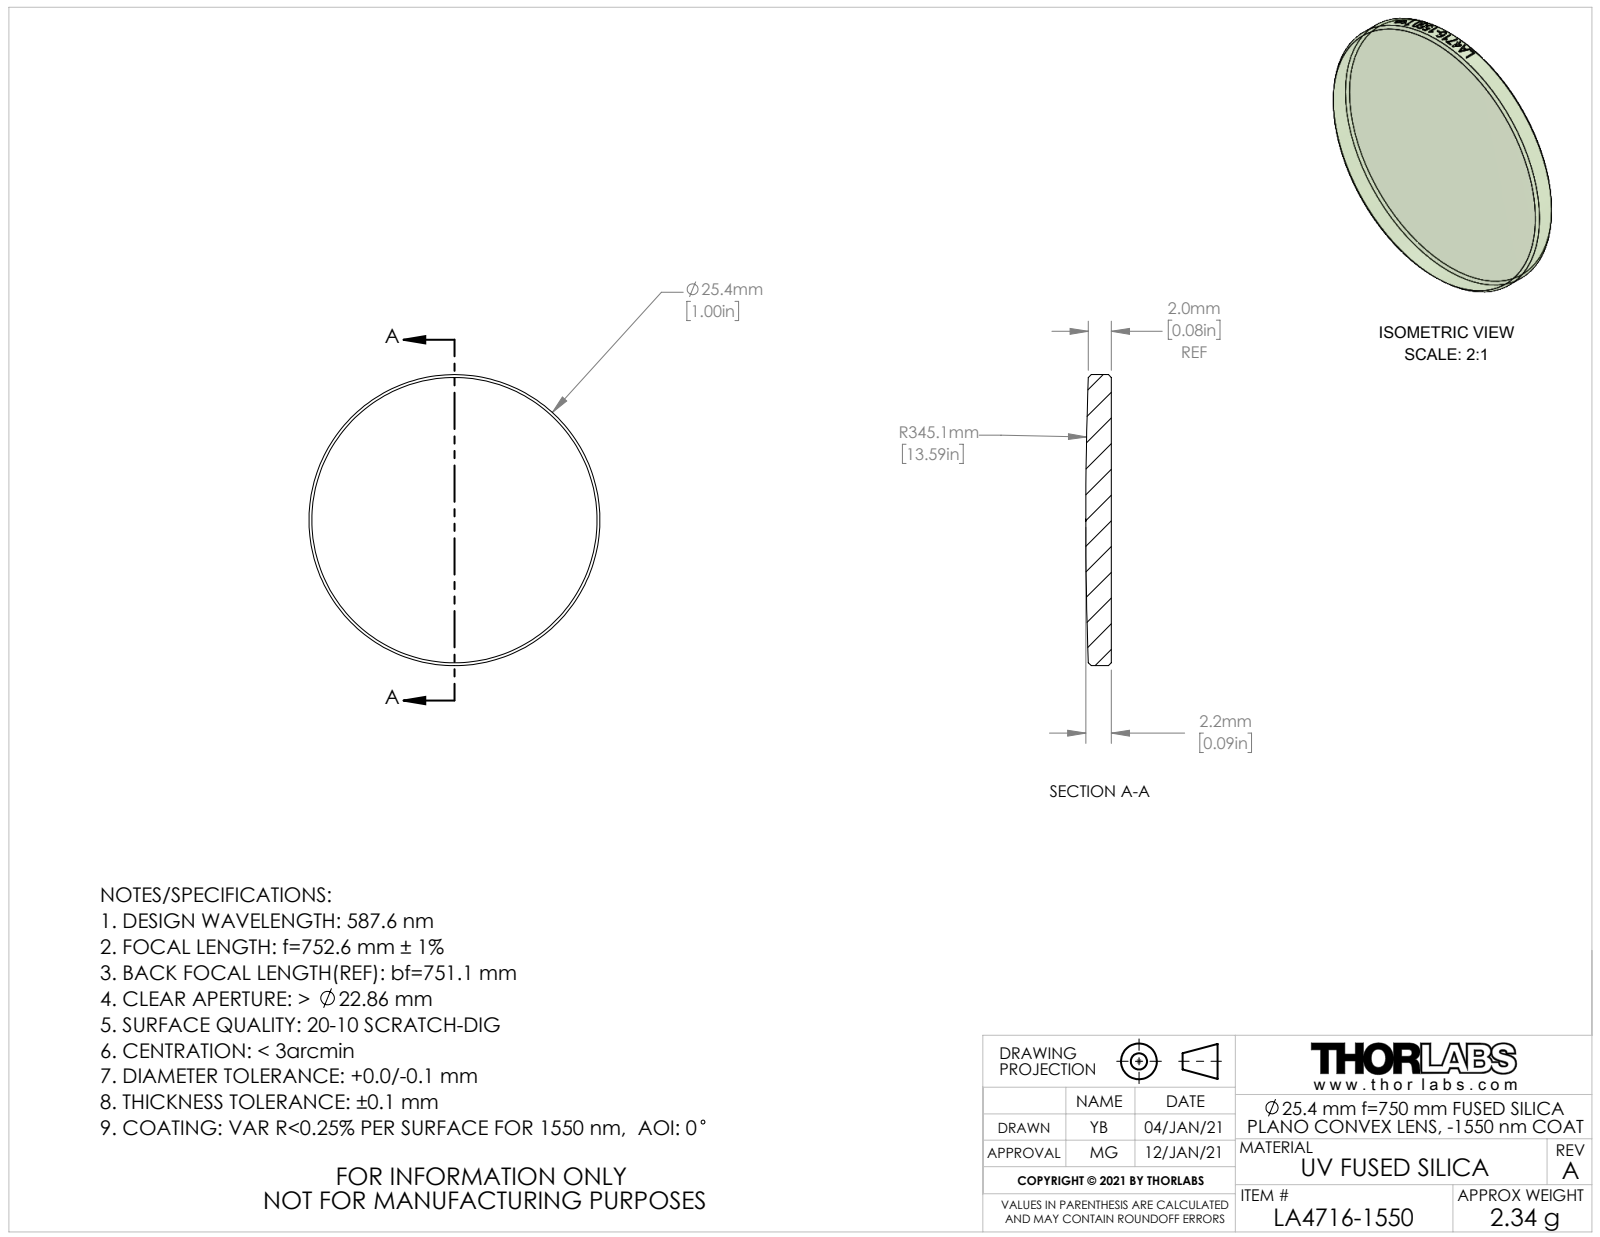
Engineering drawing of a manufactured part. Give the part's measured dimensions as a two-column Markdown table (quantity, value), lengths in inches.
| quantity | value |
| --- | --- |
| part name | CTN015959-E0W |
| STEP written by | SolidWorks 2018 (AUTOMOTIVE_DESIGN) |
| units | inches |
| bodies | 1 solid, 29 faces (1 planar, 22 cylindrical, 6 other) |
| overall size | 1 × 1 × 0.088 |
| volume | 0.065 in³ |
| surface area | 1.783 in² |
| round bosses / shafts (diameter × count) | 1 × 1 |
